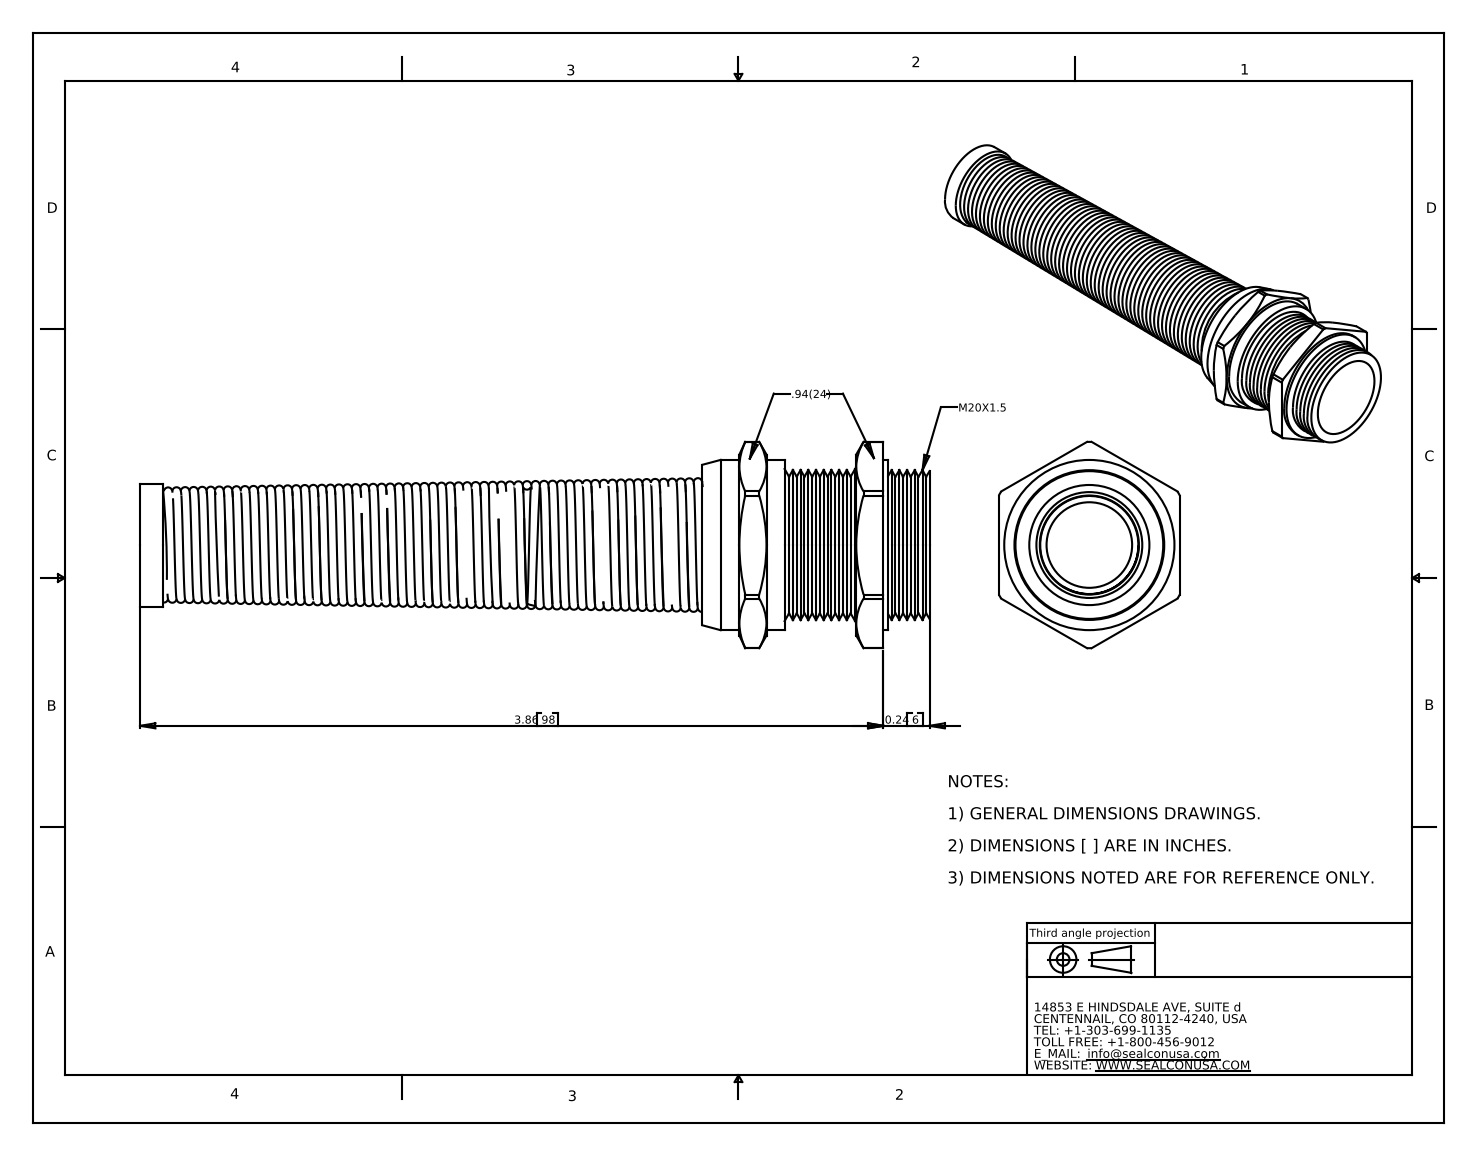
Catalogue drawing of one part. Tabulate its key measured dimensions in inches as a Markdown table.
| quantity | value |
| --- | --- |
| part name | CF22MA-BR |
| STEP written by | SolidWorks 2007 (CONFIG_CONTROL_DESIGN) |
| units | inches |
| bodies | 4 solids, 149 faces (29 planar, 34 cylindrical, 86 other) |
| overall size | 4.1 × 1.072 × 0.94 |
| volume | 0.708 in³ |
| surface area | 37.87 in² |
| round holes (diameter × count) | 0.445 × 1, 0.514 × 1, 0.55 × 1, 0.632 × 1 |
| round bosses / shafts (diameter × count) | 0.884 × 1, 0.79 × 1, 0.639 × 1 |
| partial cylindrical surfaces (radius × count) | 0.536 × 1 |
| main face-to-face distances | 0.94, 0.607, 0.192, 0.141, 0.965, 0.773, 0.799, 0.166, 2.92, 3.112 |
